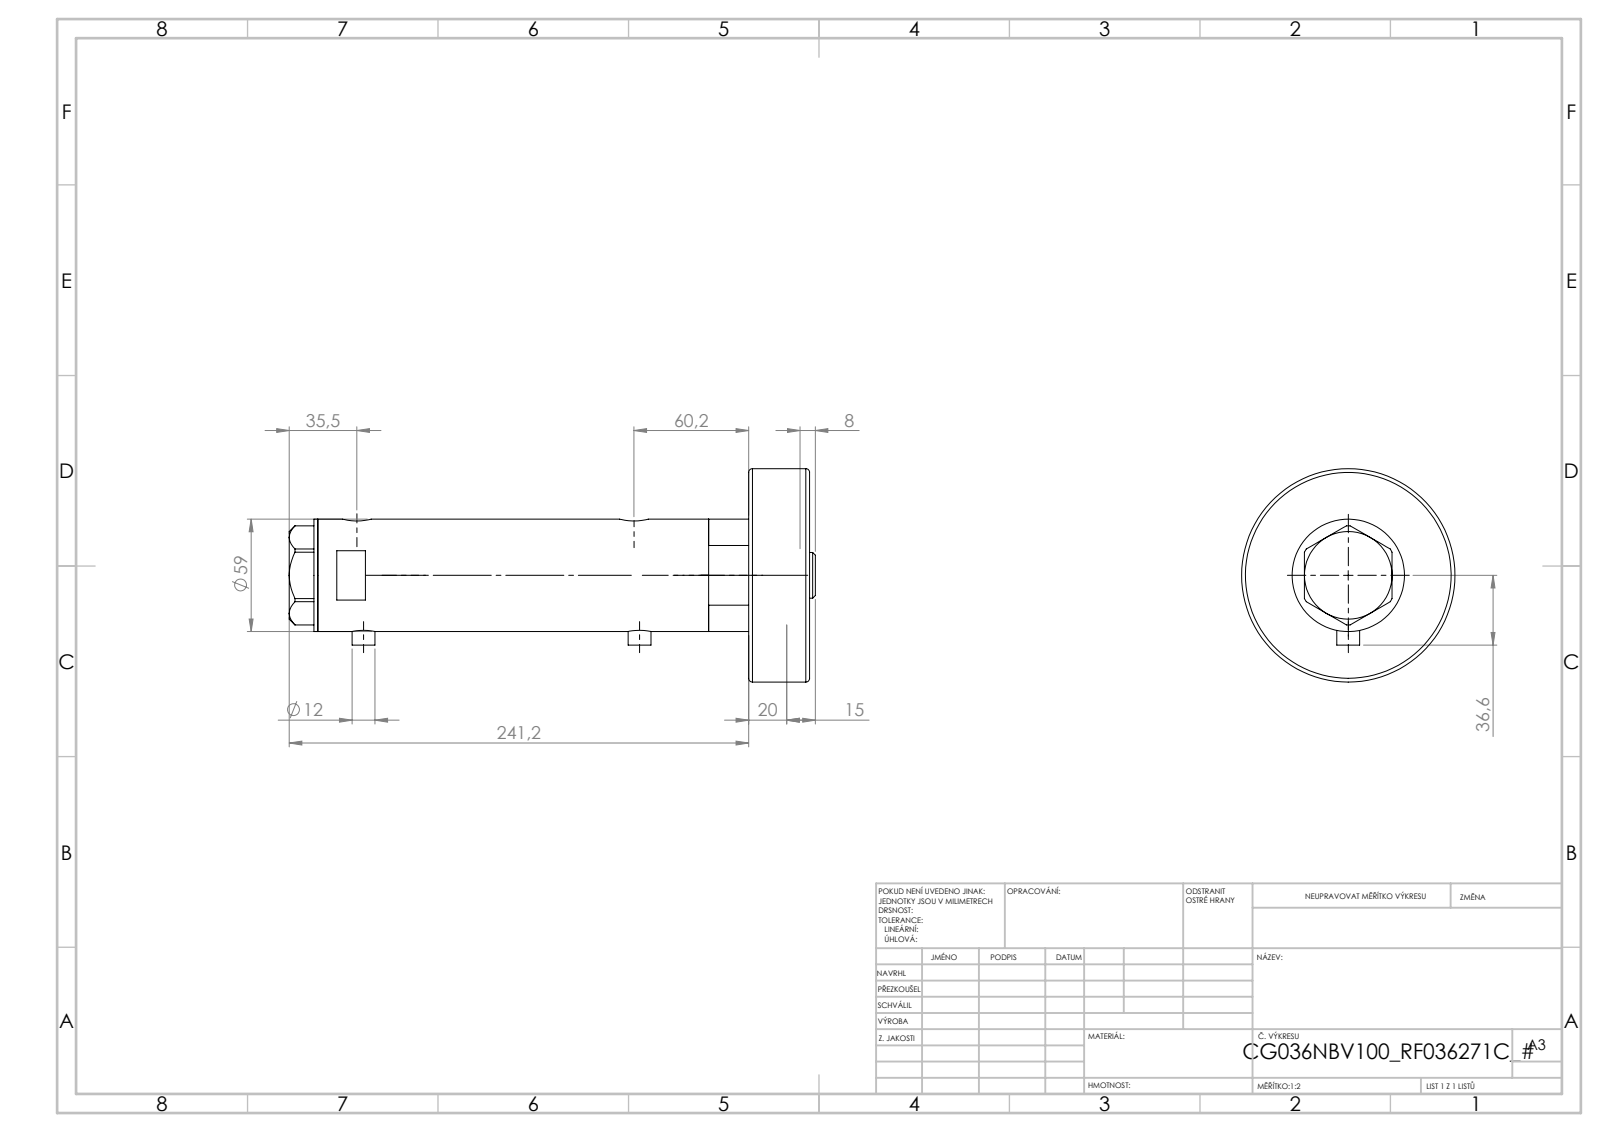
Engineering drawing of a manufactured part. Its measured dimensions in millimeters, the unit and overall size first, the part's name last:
Units: millimetres
Overall size (bounding box): 263.42 × 112 × 112
Round holes (diameter × count): ⌀5 ×2, ⌀9.73 ×2, ⌀12.5 ×2, ⌀15 ×2, ⌀8.5 ×1, ⌀25 ×1, ⌀26.5 ×1, ⌀36 ×1, ⌀40 ×1, ⌀48 ×1, ⌀52 ×1
Round bosses / shafts (diameter × count): ⌀12 ×2, ⌀112 ×1, ⌀59 ×1, ⌀46 ×1, ⌀24 ×1
Main face-to-face distances: 32.01, 210.84, 242.85, 157.34, 53.5, 85.51, 23.5, 133.84, 187.34, 219.35
Hole centre spacings: 2.9, 3.5, 132.15, 135.05, 135.65, 138.55, 2.89, 2.91
Volume: 848 598 mm³ · Surface area: 151 154 mm²
Bodies: 5 solids, 136 faces (55 planar, 57 cylindrical, 24 other)
Part name (STEP PRODUCT): V270CG_MIDDLE; V270CG_271C; V270CG_BACK; V270CG_FRONT (+1 more)
STEP written by: SolidWorks 2019 (CONFIG_CONTROL_DESIGN)
